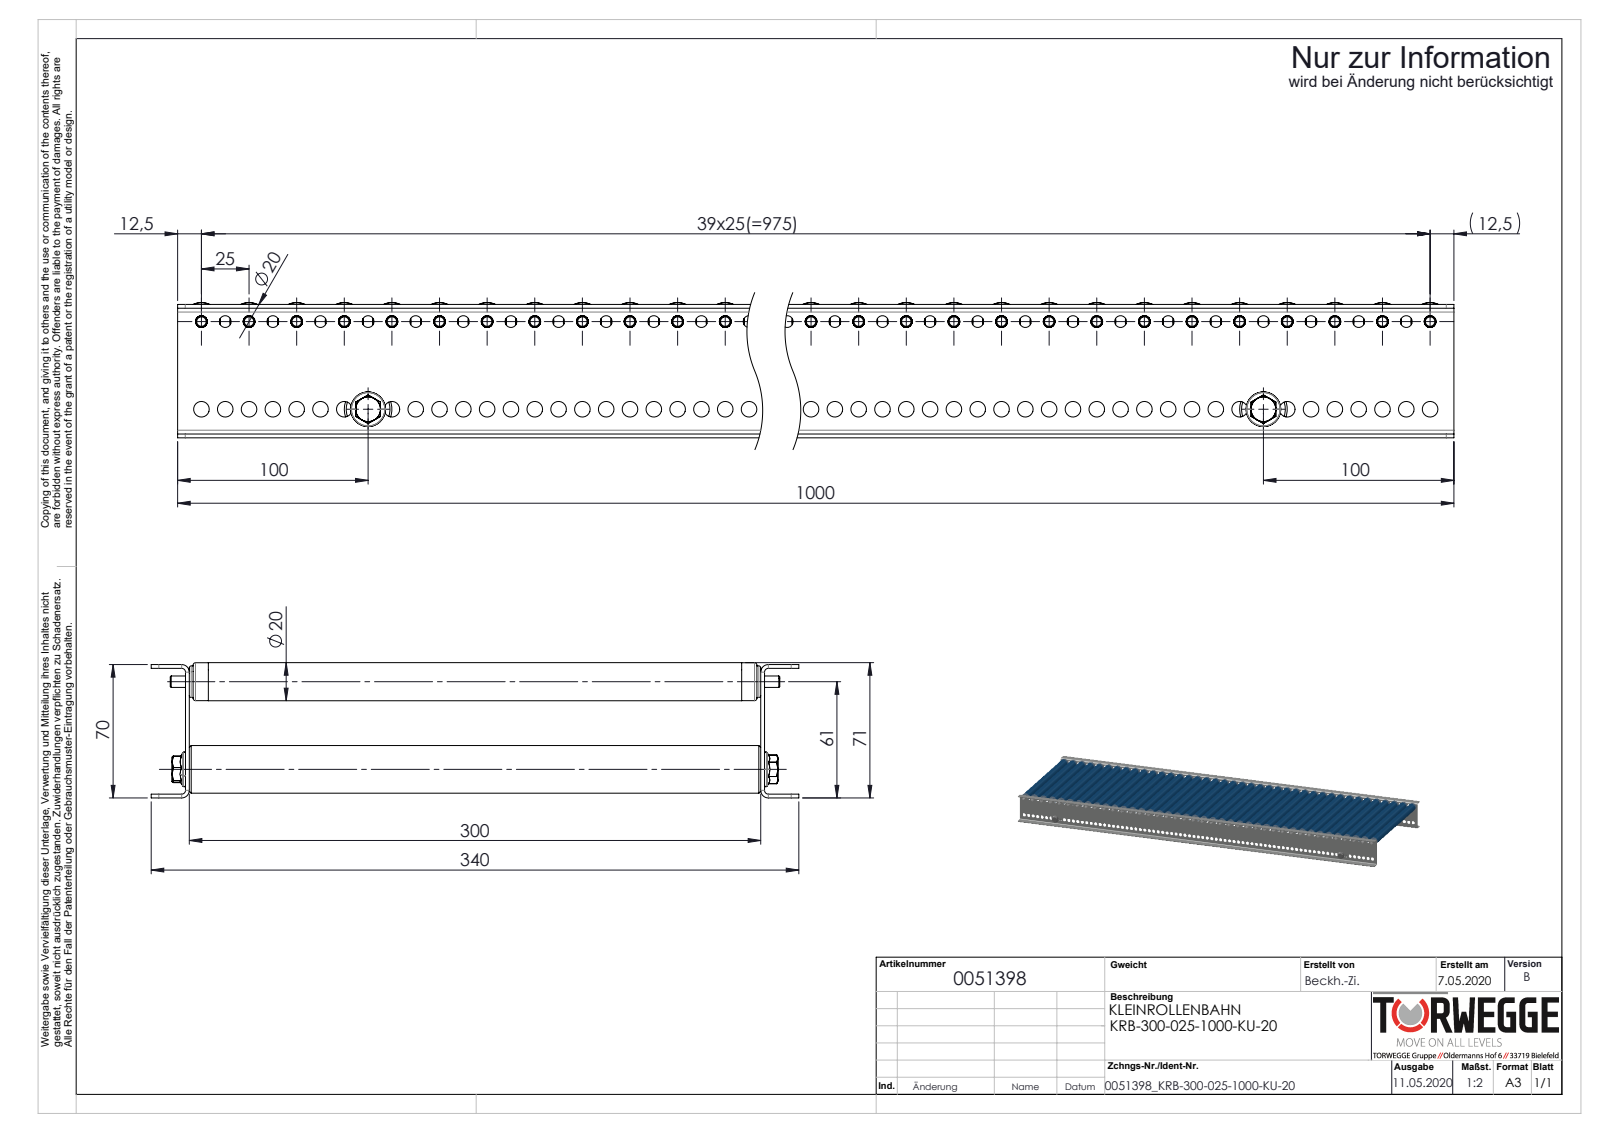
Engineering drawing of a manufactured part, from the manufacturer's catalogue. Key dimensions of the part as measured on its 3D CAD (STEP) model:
Part name (STEP PRODUCT): S100994_Sperrzahnschraube_M08x16-8.8-A2K; 0026257_TYP-KUT50-20X1,5-6; 0017012_Tragrollenrohr-Ø20x1,5KU_KFG_L280; Profil_KRB-20x70x20x2_KFG_S100204_U-PROFIL-20-70-20-2-KRB-20-L=1000 (+4 more)
STEP written by: SolidWorks 2020 (AUTOMOTIVE_DESIGN)
Units: millimetres
Bodies: 252 solids, 10672 faces (3560 planar, 3968 cylindrical, 3144 other)
Overall size (bounding box): 1000 × 340 × 71
Volume: 2 115 000 mm³ · Surface area: 2 404 000 mm²
Round holes (diameter × count): ⌀6.2 ×79, ⌀8.2 ×79, ⌀6.1 ×40, ⌀12.4 ×40, ⌀13.2 ×40, ⌀14.6 ×40, ⌀16.2 ×40, ⌀17 ×40, ⌀17.2 ×40, ⌀6.8 ×2, ⌀21 ×2
Round bosses / shafts (diameter × count): ⌀20 ×40, ⌀19.9 ×40, ⌀17.1 ×40, ⌀16.8 ×40, ⌀16.5 ×40, ⌀11.4 ×40, ⌀11.1 ×40, ⌀10.2 ×40
Partial cylindrical surfaces — rounded edges, fillets, slot ends (radius × count): R4.05 ×40, R4 ×8, R2 ×4
Main face-to-face distances: 2, 302, 68, 300, 304, 66, 70, 292, 10, 12
Hole centre spacings: 12.5, 25, 37.5, 50, 62.5, 75, 87.5, 100
